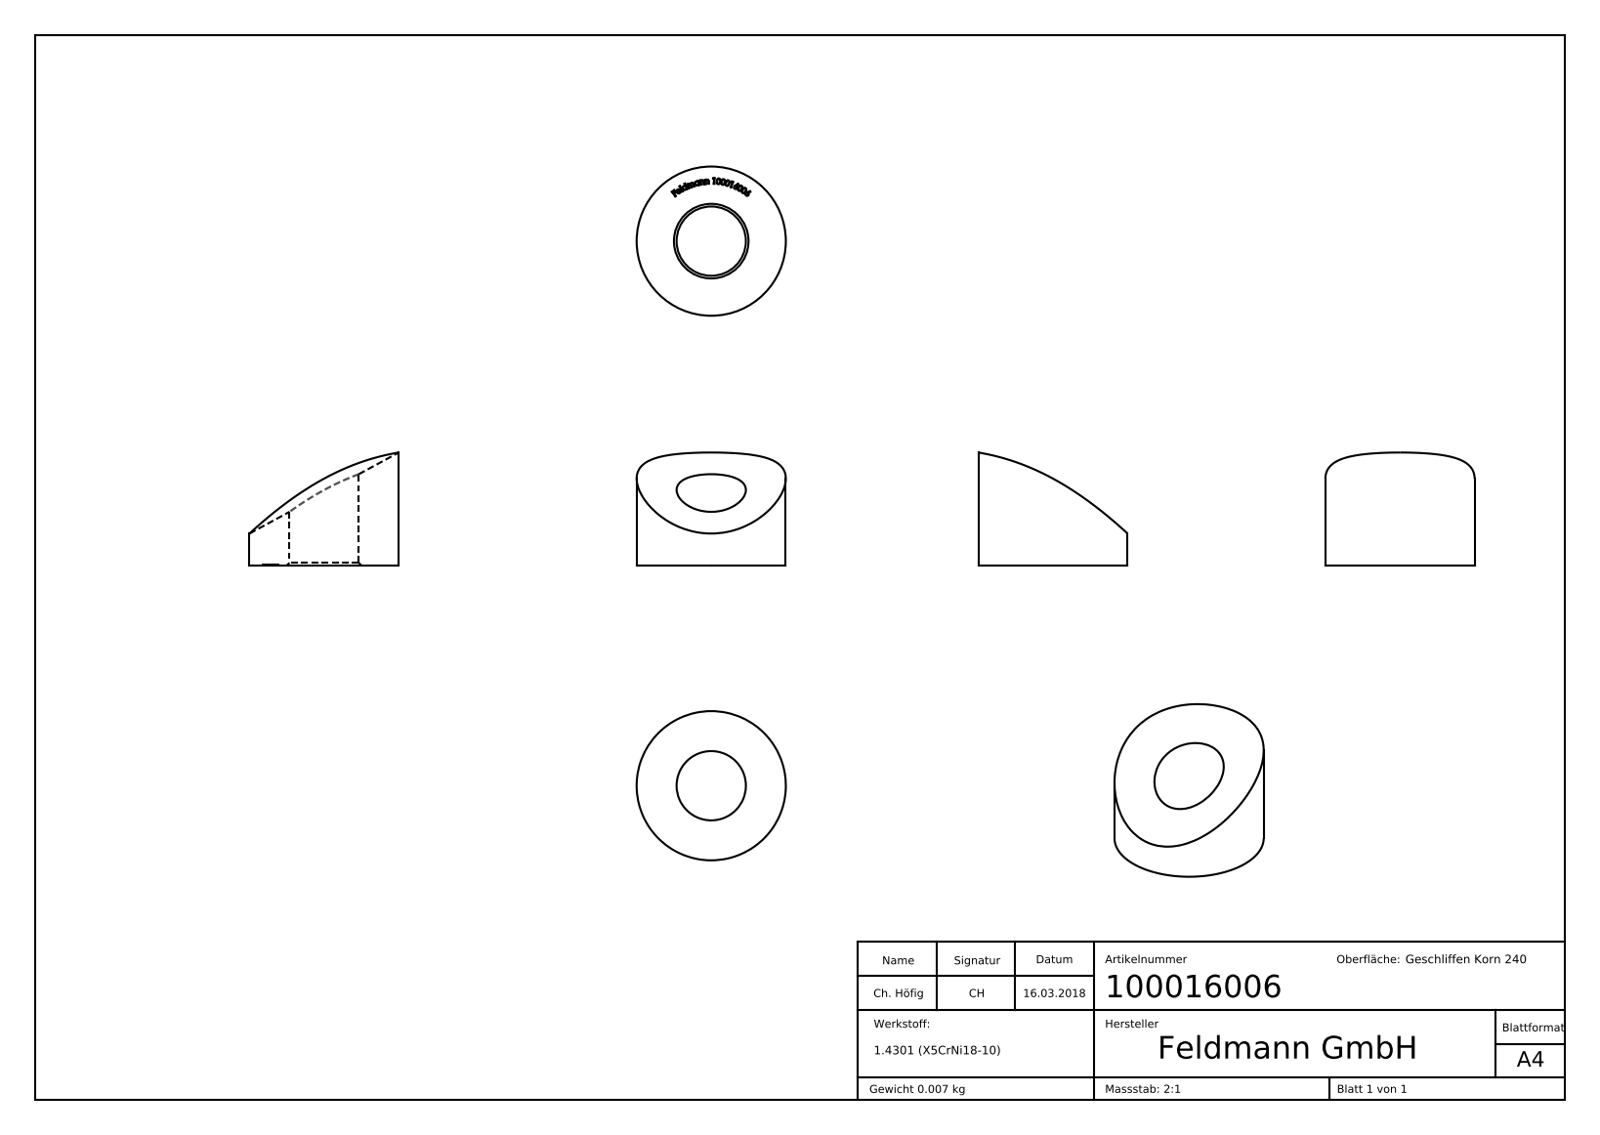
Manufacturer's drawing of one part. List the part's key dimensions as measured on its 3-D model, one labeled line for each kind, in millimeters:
Part name (STEP PRODUCT): 100016006
STEP written by: SolidWorks 2015 (CONFIG_CONTROL_DESIGN)
Units: millimetres
Bodies: 1 solid, 218 faces (100 planar, 5 cylindrical, 113 other)
Overall size (bounding box): 14 × 14 × 10.6
Volume: 869 mm³ · Surface area: 732 mm²
Round holes (diameter × count): ⌀6.5 ×1
Round bosses / shafts (diameter × count): ⌀14 ×1
Partial cylindrical surfaces — rounded edges, fillets, slot ends (radius × count): R21.2 ×1
Main face-to-face distances: 0.53, 0.34, 0.48, 0.31, 0.58, 0.39, 0.32, 0.47, 0.54, 0.52
